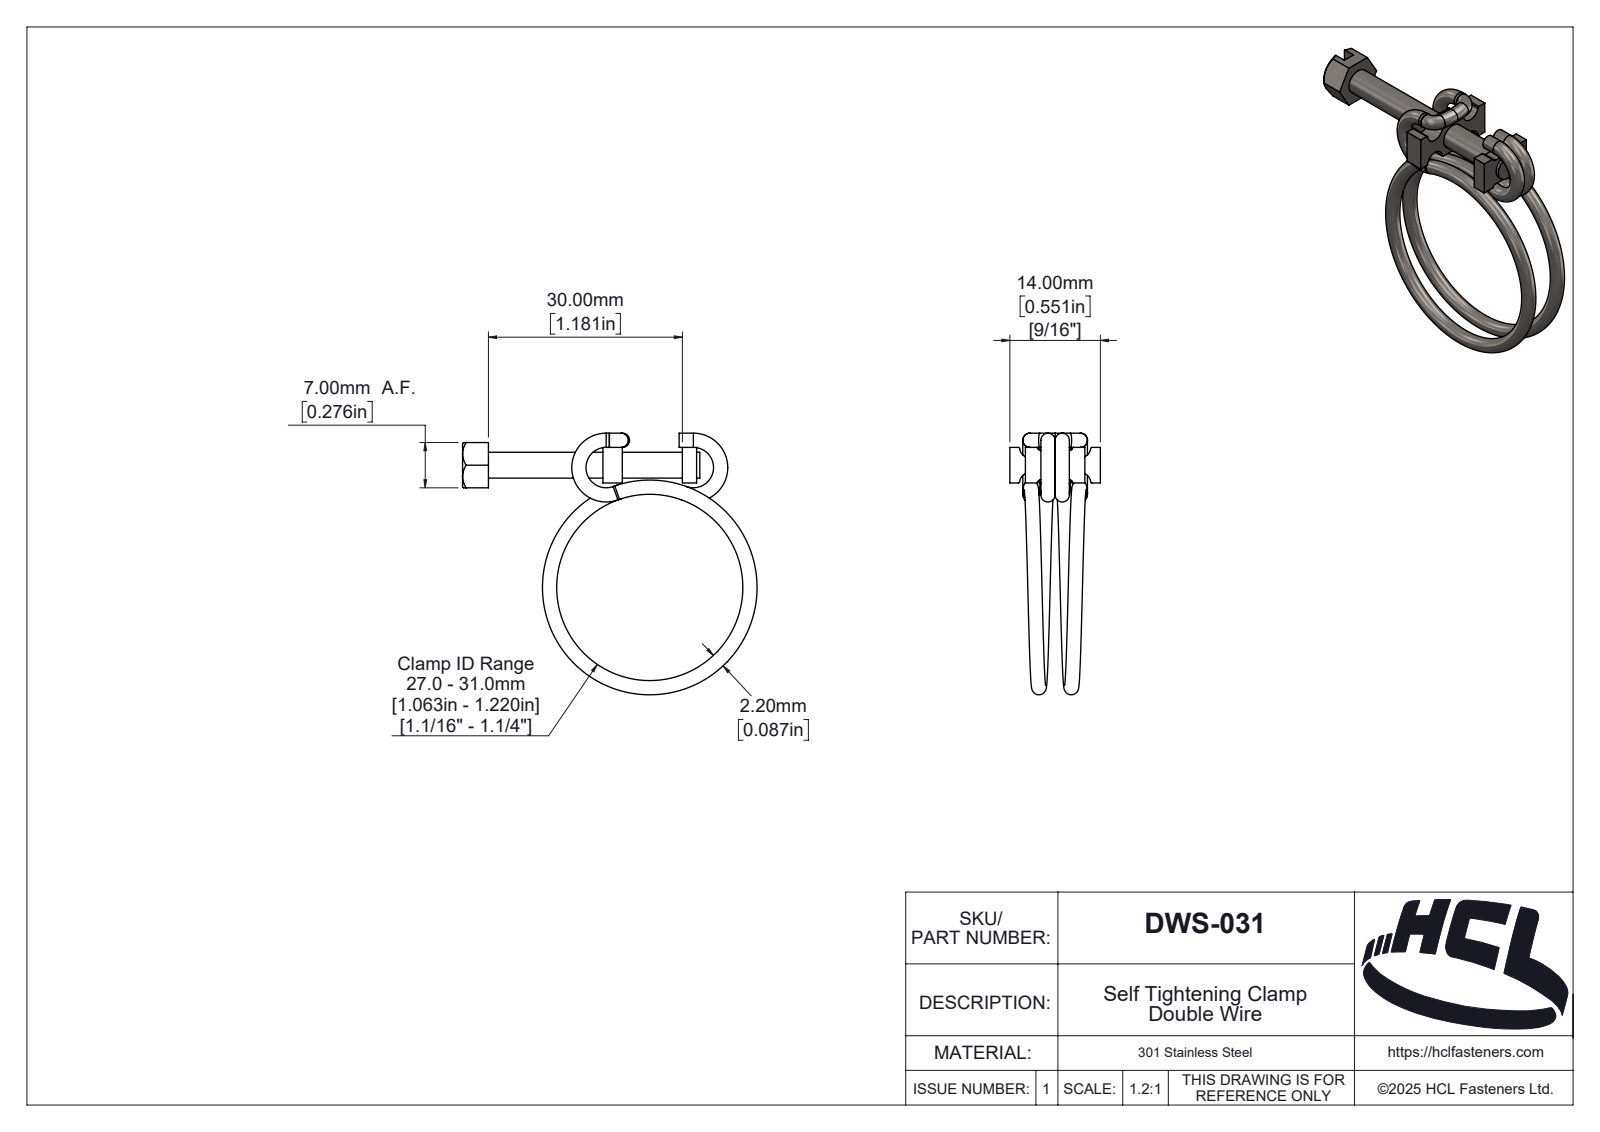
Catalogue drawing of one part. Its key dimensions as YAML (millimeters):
part_name: "DWS-031"
step_written_by: "SolidWorks 2025 (AUTOMOTIVE_DESIGN)"
units: millimeters
bodies: {solids: 6, faces: 209, planar: 51, cylindrical: 74, other: 84}
overall_size: [45.55, 40.45, 14]
volume: 1874
surface_area: 3074
round_holes:
  - {diameter: 4, count: 1}
round_bosses_or_shafts:
  - {diameter: 2.2, count: 4}
partial_cylinders:
  - {radius: 0.2, count: 12}
  - {radius: 0.5, count: 4}
  - {radius: 1.6, count: 4}
  - {radius: 0.4, count: 1}
  - {radius: 0.51, count: 1}
  - {radius: 0.53, count: 1}
  - {radius: 0.64, count: 1}
  - {radius: 0.91, count: 1}
face_to_face_distances: [2, 3, 20.72, 7, 0.5, 14.48, 11.48, 12.28, 9.28, 2.2]
